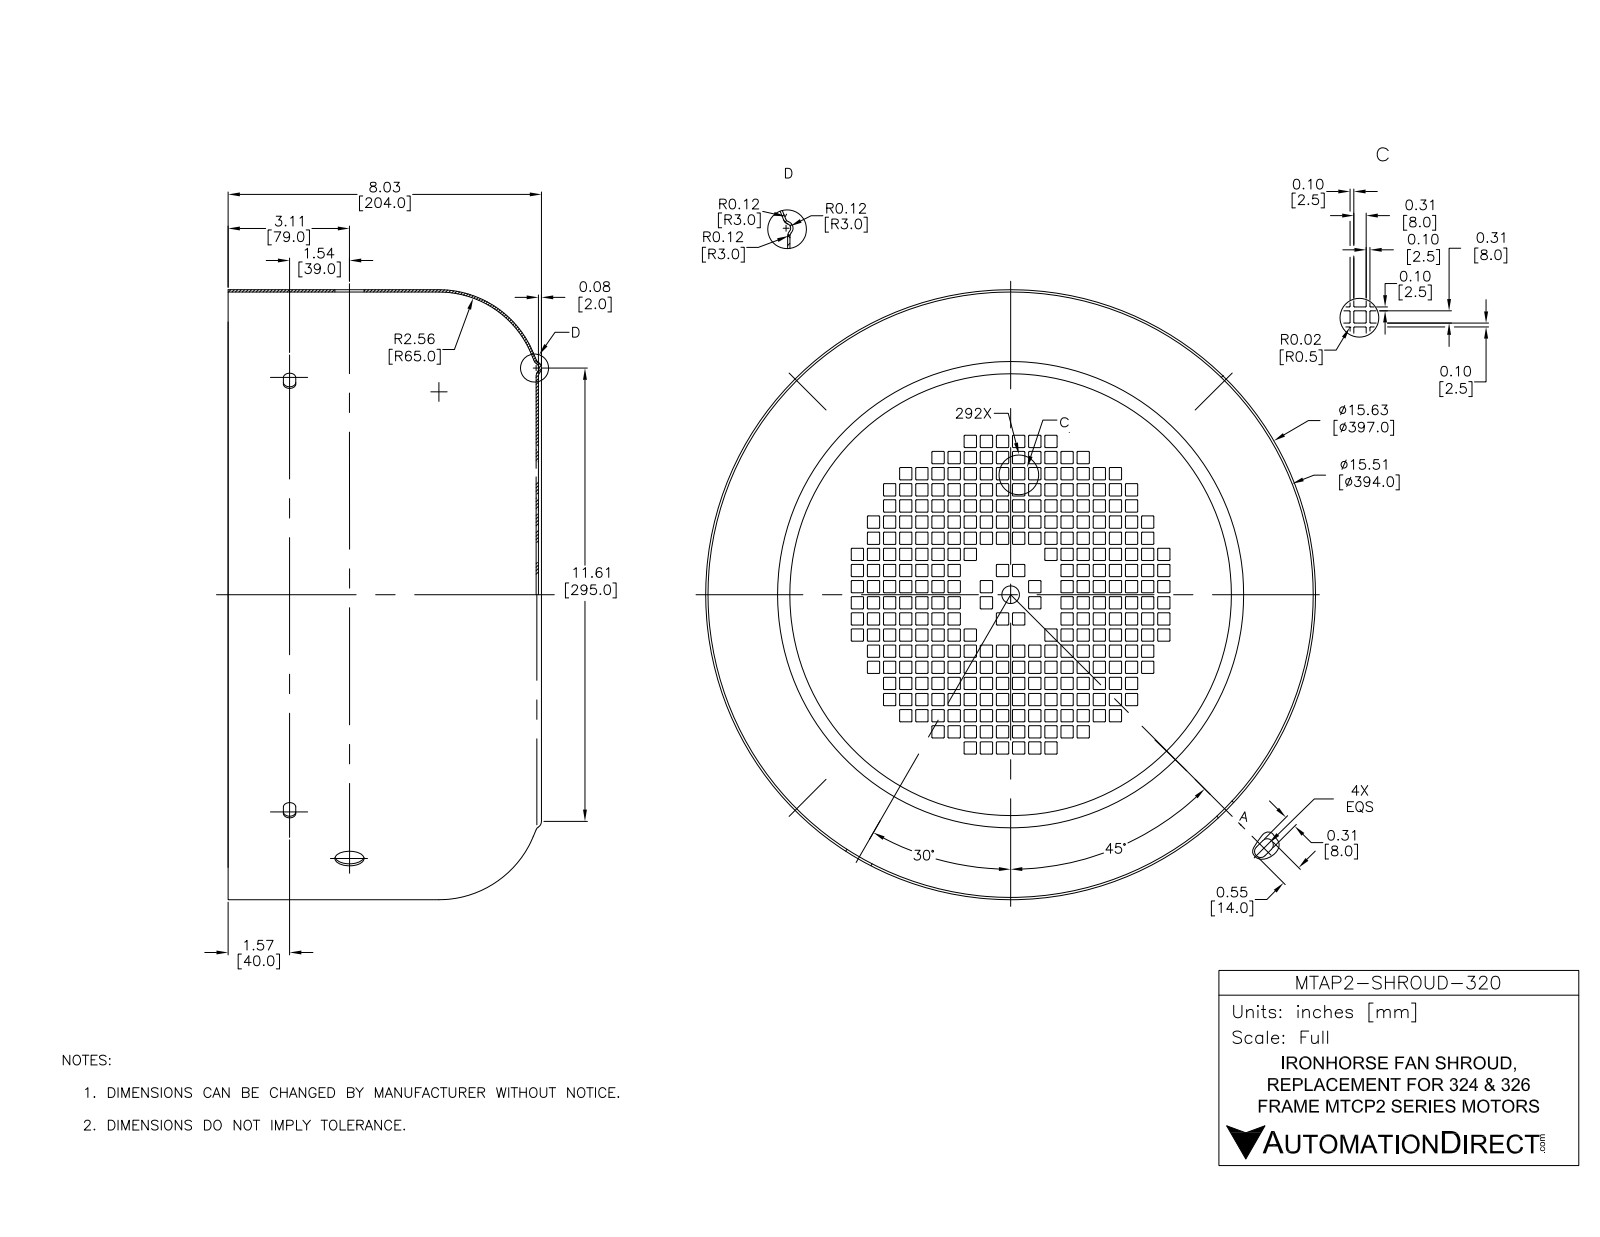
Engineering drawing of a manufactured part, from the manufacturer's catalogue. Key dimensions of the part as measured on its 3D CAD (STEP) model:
Part name (STEP PRODUCT): MTAP2-SHROUD-320
STEP written by: SolidWorks 2017 (AUTOMOTIVE_DESIGN)
Units: inches
Bodies: 1 solid, 1519 faces (1474 planar, 25 cylindrical, 20 other)
Overall size (bounding box): 15.63 × 15.63 × 8.031
Volume: 31.34 in³ · Surface area: 1 059 in²
Round holes (diameter × count): ⌀0.748 ×2, ⌀0.398 ×1, ⌀15.394 ×1, ⌀15.512 ×1
Round bosses / shafts (diameter × count): ⌀15.63 ×1
Partial cylindrical surfaces — rounded edges, fillets, slot ends (radius × count): R0.157 ×7
Main face-to-face distances: 0.059, 0.039, 0.02, 5.276, 2.638, 2.677, 2.697, 7.913, 7.953, 7.972
